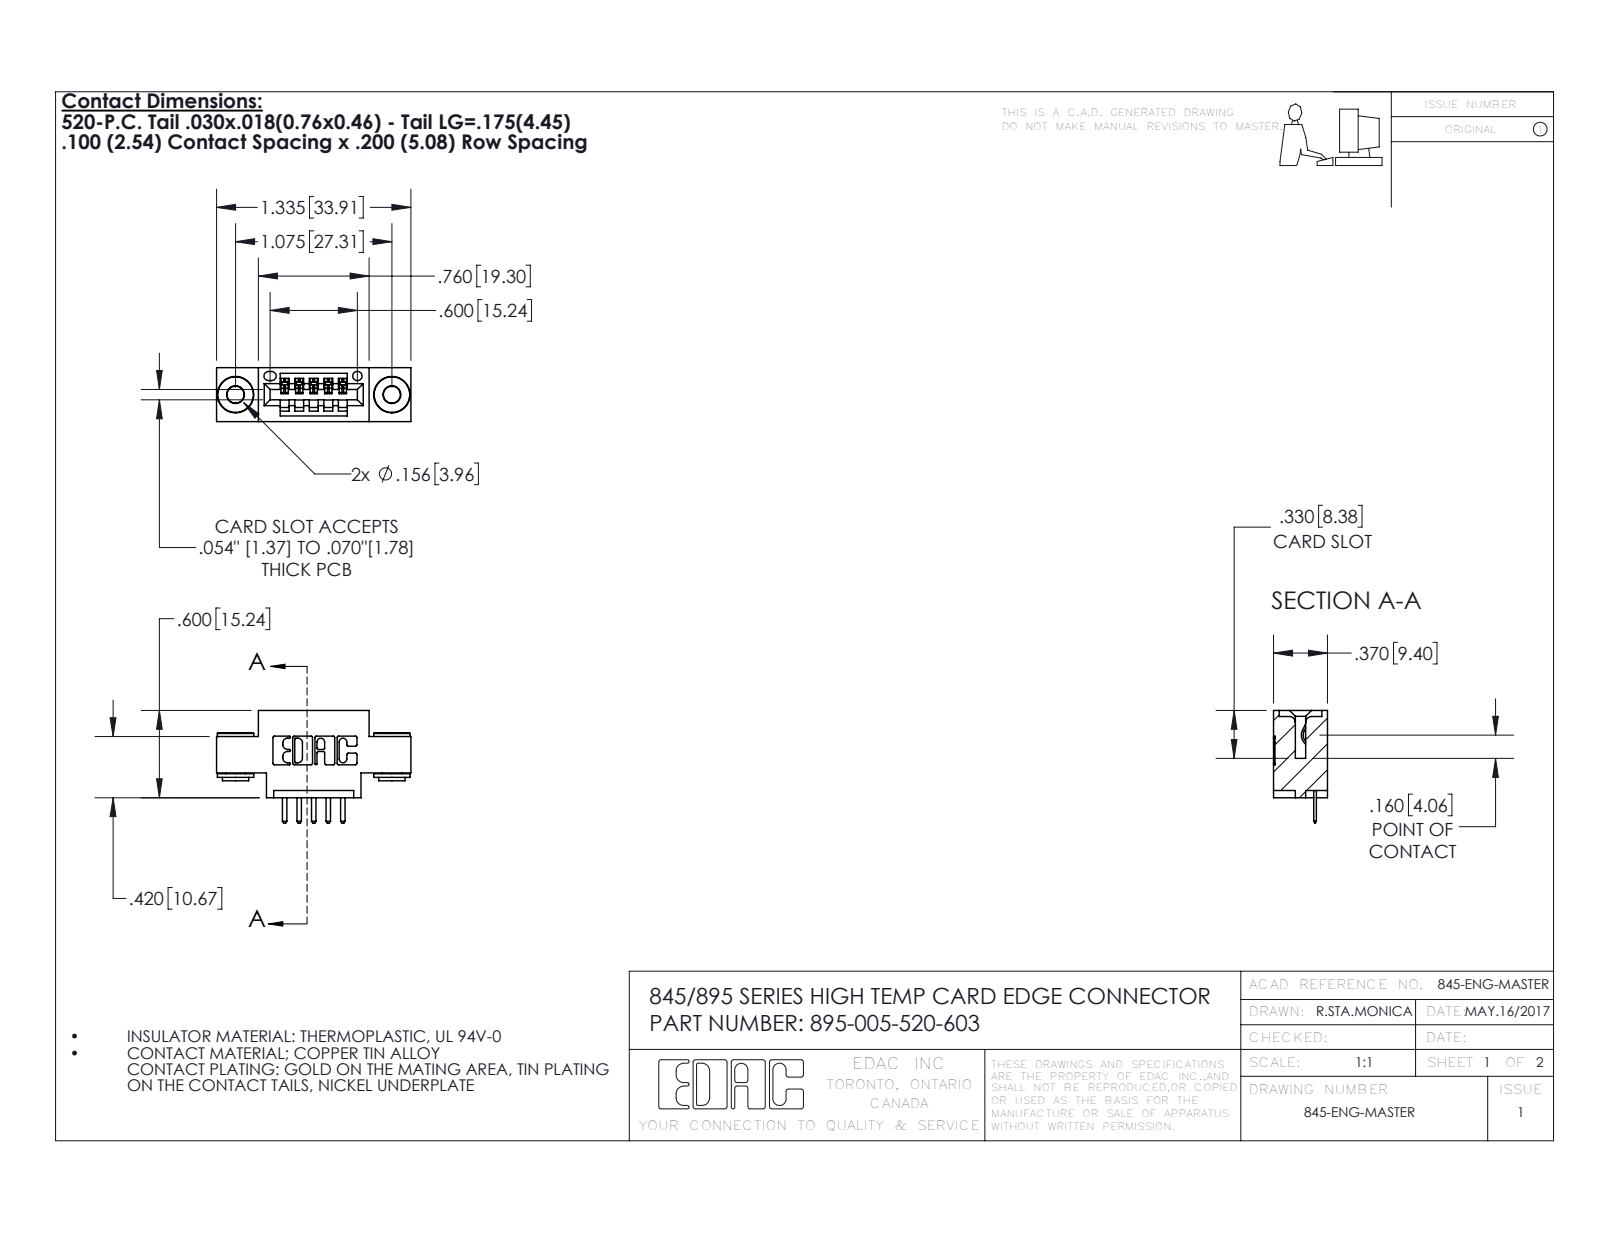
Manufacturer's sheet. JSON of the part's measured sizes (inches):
{"part_name": "345-250-002_345-250-002-102; 345 Part_0.170 Offset - 0.156 Dia-TH; 395-005-520-603; 345-292-001_345-293-120", "step_written_by": "SolidWorks 2016 (CONFIG_CONTROL_DESIGN)", "units": "inches", "bodies": {"solids": 8, "faces": 478, "planar": 304, "cylindrical": 166, "other": 8}, "overall_size": [1.335, 0.775, 0.37], "volume_in3": 0.171, "surface_area_in2": 5.463, "round_holes": [[0.116, 2], [0.156, 2], [0.064, 1]], "round_bosses_or_shafts": [[0.25, 2], [0.18, 2], [0.136, 2]], "partial_cylinders_radius": [[0.01, 22], [0.01, 12], [0.006, 10], [0.007, 6], [0.031, 6], [0.026, 3], [0.031, 2], [0.04, 2]], "face_to_face_distances": [0.37, 0.2, 0.1, 0.072, 0.298, 0.25, 0.025, 0.06, 0.55, 0.255], "hole_center_spacings": [0.27, 0.847, 1.075]}
